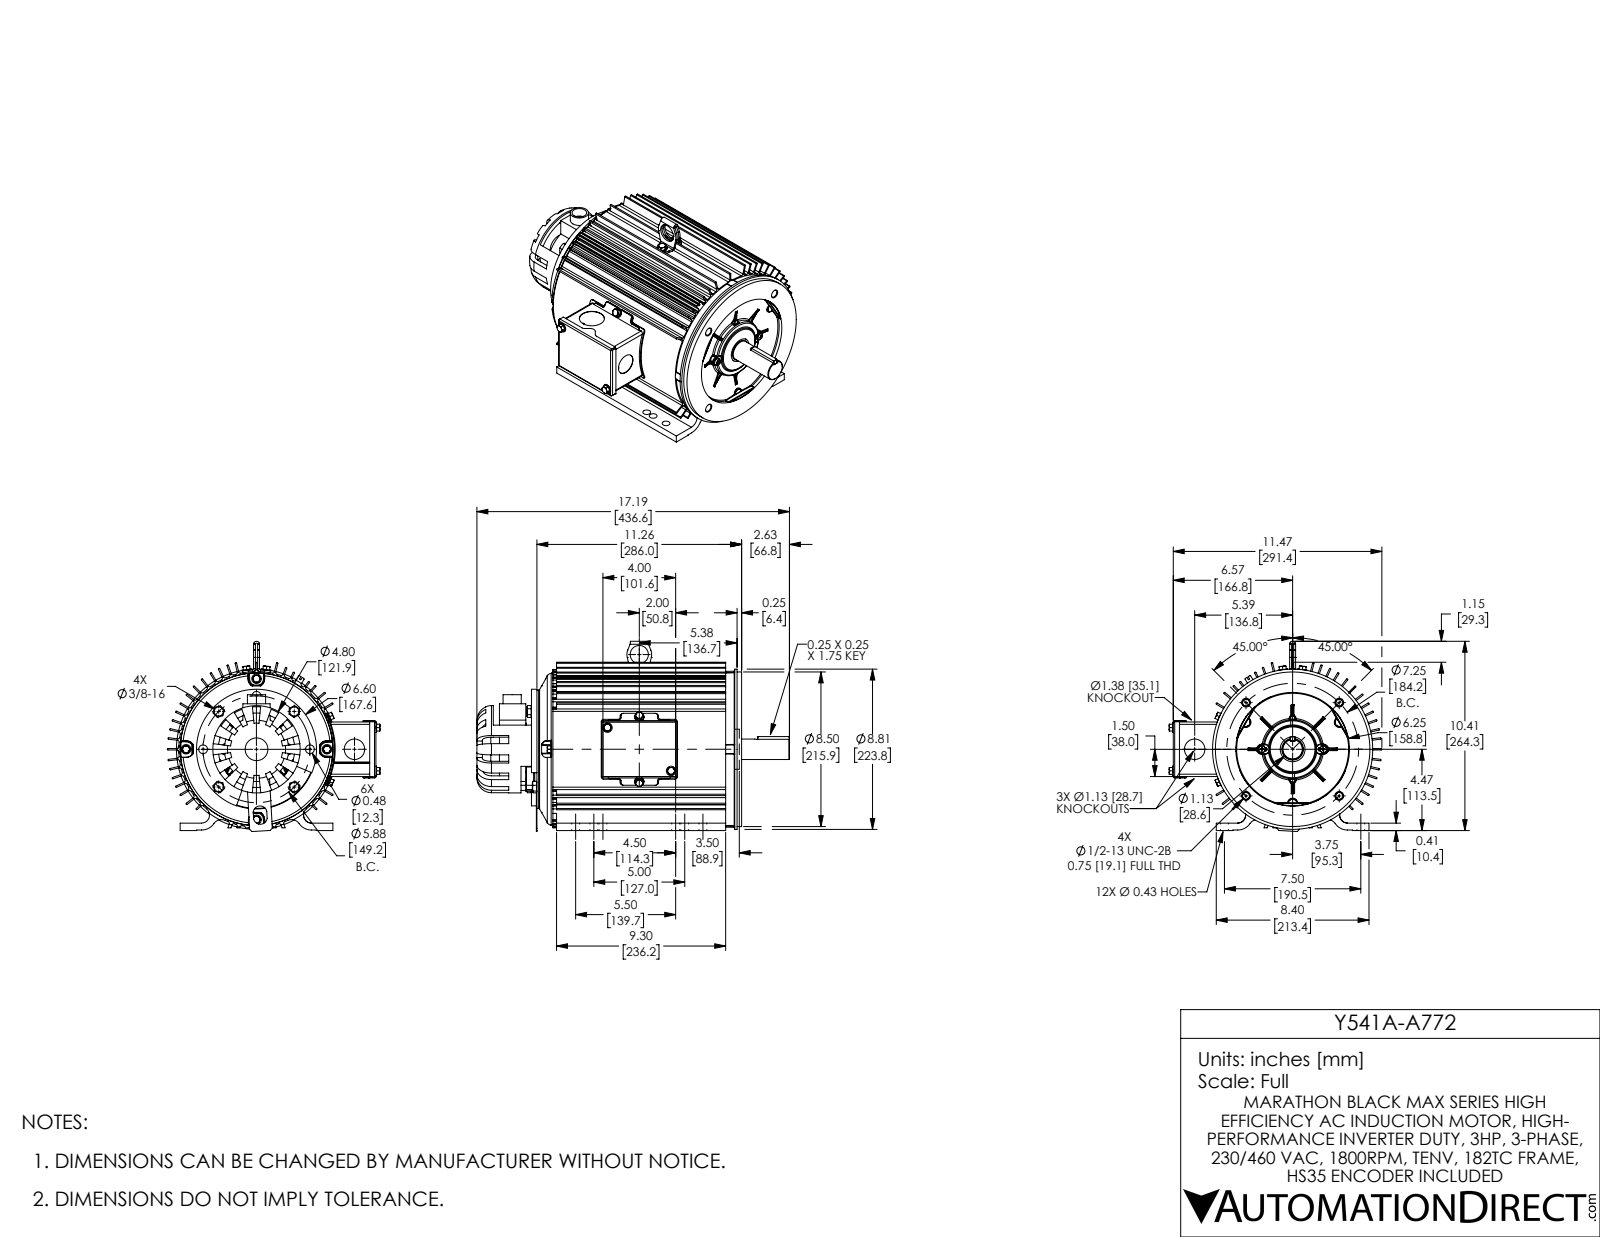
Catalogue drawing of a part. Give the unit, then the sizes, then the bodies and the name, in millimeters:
Units: millimetres
Overall size (bounding box): 436.7 × 297.1 × 265.6
Round holes (diameter × count): ⌀3.8 ×24, ⌀10.9 ×12, ⌀12.3 ×6, ⌀5.7 ×5, ⌀5.1 ×4, ⌀6.8 ×4, ⌀7.1 ×4, ⌀8 ×4, ⌀10.7 ×4, ⌀3.9 ×2, ⌀5.3 ×2, ⌀5.4 ×2
Round bosses / shafts (diameter × count): ⌀13.2 ×10, ⌀6.4 ×10, ⌀12.7 ×4, ⌀9.5 ×4, ⌀9.5 ×2, ⌀7.8 ×2, ⌀4.8 ×2, ⌀223.8 ×1
Partial cylindrical surfaces — rounded edges, fillets, slot ends (radius × count): R0.8 ×118, R1.5 ×101, R2.5 ×78, R1 ×33, R1.3 ×23, R3.3 ×16, R0.6 ×12, R6.4 ×7
Main face-to-face distances: 2, 1.2, 2, 10.4, 286, 3.3, 7.6, 22.4, 263.7, 76.2
Hole centre spacings: 30.2, 7.9, 30.2, 36.8, 48, 52.3, 58.4, 23.1
Volume: 2 823 000 mm³ · Surface area: 1 170 000 mm²
Bodies: 31 solids, 4757 faces (976 planar, 1132 cylindrical, 2649 other)
Part name (STEP PRODUCT): Y541A-A772
STEP written by: SolidWorks 2021 (AUTOMOTIVE_DESIGN)
